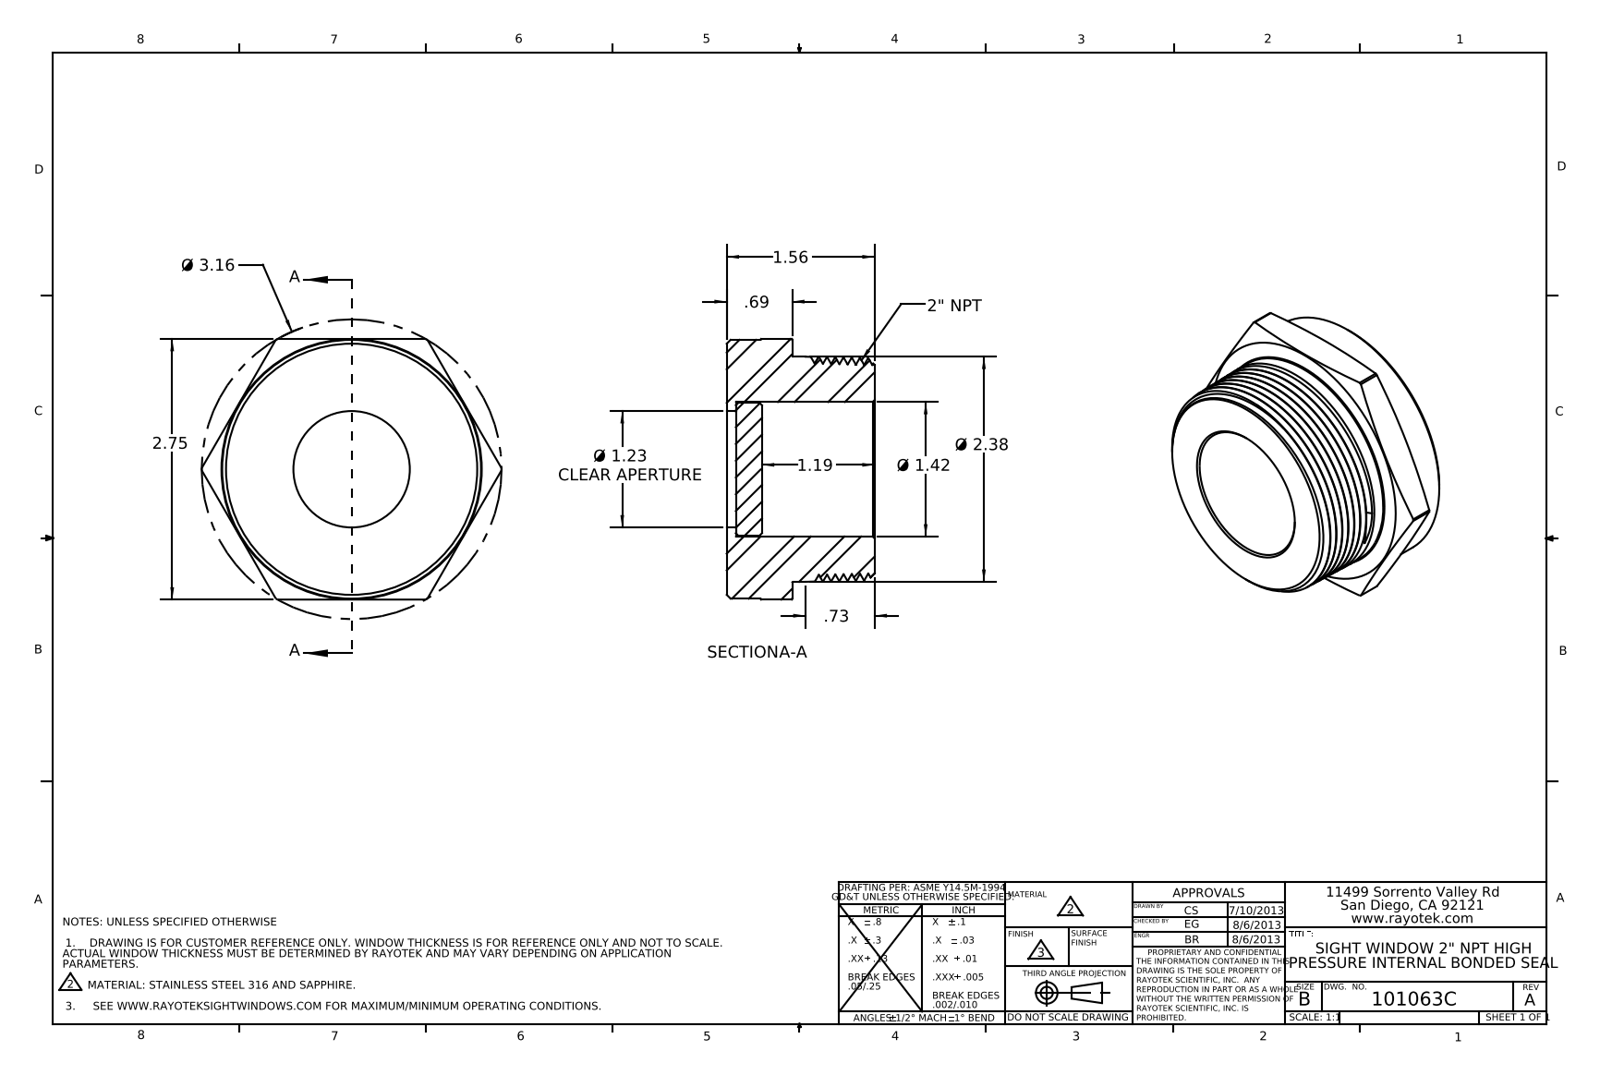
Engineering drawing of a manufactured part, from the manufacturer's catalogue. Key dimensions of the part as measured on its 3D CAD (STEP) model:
Part name (STEP PRODUCT): 101063; 402063; 403063
STEP written by: SolidWorks 2012 (AUTOMOTIVE_DESIGN)
Units: inches
Bodies: 2 solids, 71 faces (15 planar, 17 cylindrical, 39 other)
Overall size (bounding box): 3.163 × 2.75 × 1.56
Volume: 5.874 in³ · Surface area: 37.24 in²
Round holes (diameter × count): ⌀1.228 ×1, ⌀1.42 ×1
Round bosses / shafts (diameter × count): ⌀2.73 ×1, ⌀2.375 ×1, ⌀1.41 ×1
Partial cylindrical surfaces — rounded edges, fillets, slot ends (radius × count): R1.582 ×1
Main face-to-face distances: 1.56, 0.096, 1.464, 0.371, 0.276, 1.189, 2.75, 0.69, 0.594, 0.319
